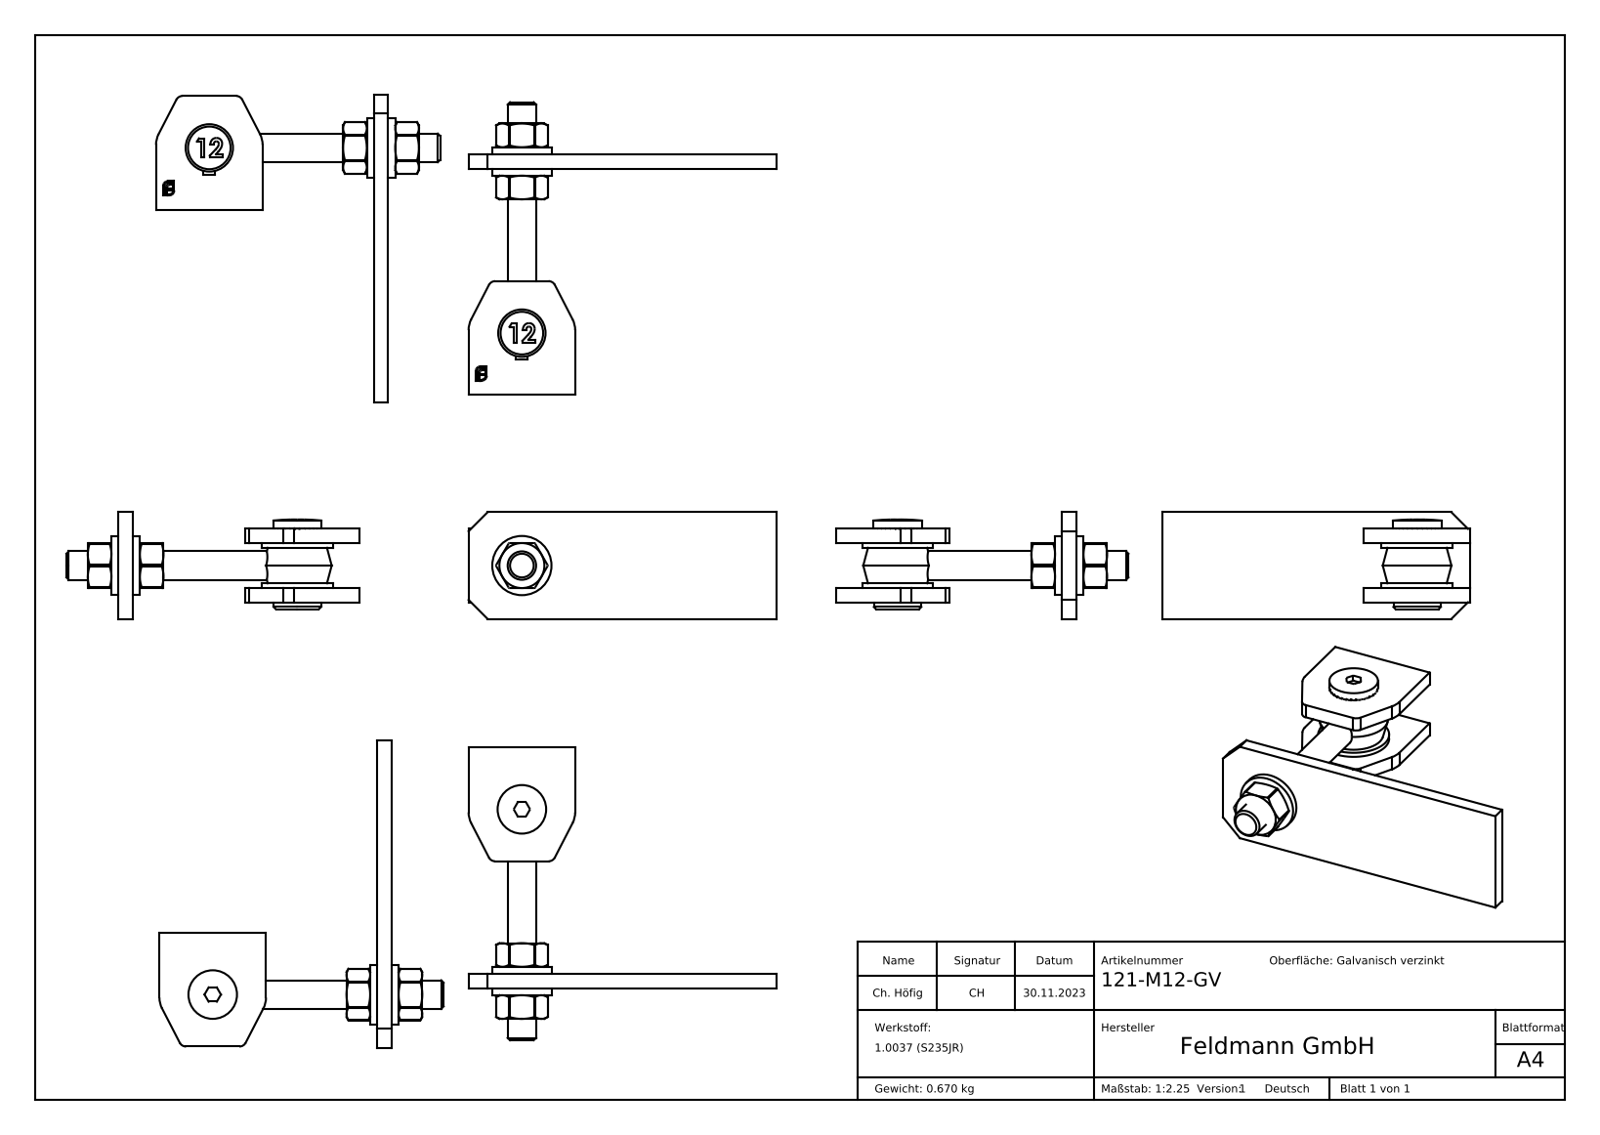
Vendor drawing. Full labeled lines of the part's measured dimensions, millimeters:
Part name (STEP PRODUCT): 121-M12-GV; Torband Teil4_121-M12-GV Teil4; Torband Teil3_121-M12-GV Teil3; DIN 934 M4-M20_DIN 934 M12 (+6 more)
STEP written by: SolidWorks 2018 (CONFIG_CONTROL_DESIGN)
Units: millimetres
Bodies: 12 solids, 553 faces (360 planar, 41 cylindrical, 152 other)
Overall size (bounding box): 130 × 123.55 × 45
Volume: 85 682 mm³ · Surface area: 40 531 mm²
Round holes (diameter × count): ⌀5 ×1, ⌀10.2 ×1, ⌀12.5 ×1, ⌀13 ×1, ⌀13.3 ×1
Round bosses / shafts (diameter × count): ⌀30 ×1, ⌀25 ×1, ⌀20.5 ×1, ⌀20 ×1, ⌀12 ×1, ⌀11.7 ×1, ⌀6 ×1
Partial cylindrical surfaces — rounded edges, fillets, slot ends (radius × count): R0.5 ×6, R3 ×2, R7 ×2, R10 ×2
Main face-to-face distances: 6, 25, 19, 15, 31, 8, 23, 2, 17, 13
